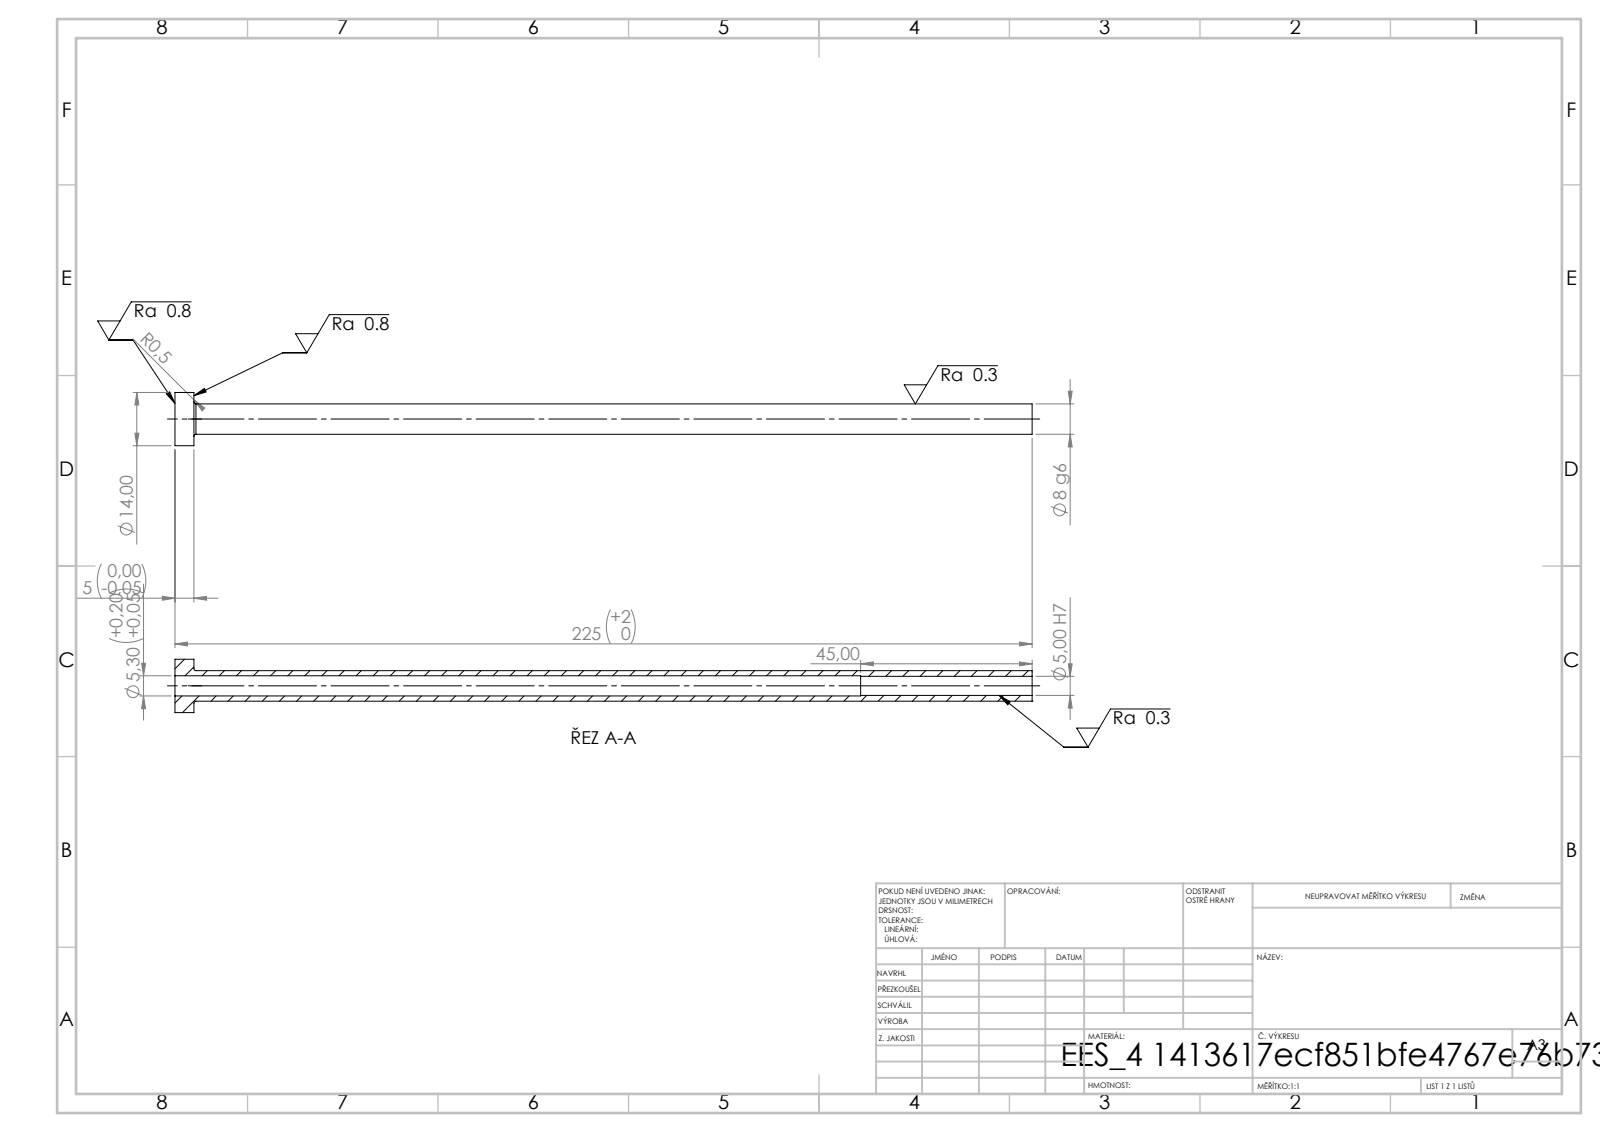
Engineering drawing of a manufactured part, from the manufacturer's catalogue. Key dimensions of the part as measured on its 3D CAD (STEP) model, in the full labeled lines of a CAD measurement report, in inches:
STEP written by: SolidWorks 2019 (CONFIG_CONTROL_DESIGN)
Units: inches
Bodies: 1 solid, 14 faces (4 planar, 8 cylindrical, 2 other)
Overall size (bounding box): 8.858 × 0.551 × 0.551
Volume: 0.426 in³ · Surface area: 15.06 in²
Round holes (diameter × count): ⌀0.197 ×1, ⌀0.209 ×1
Round bosses / shafts (diameter × count): ⌀0.551 ×1, ⌀0.315 ×1
Main face-to-face distances: 0.197, 8.858, 8.661, 7.087, 6.89, 1.772
